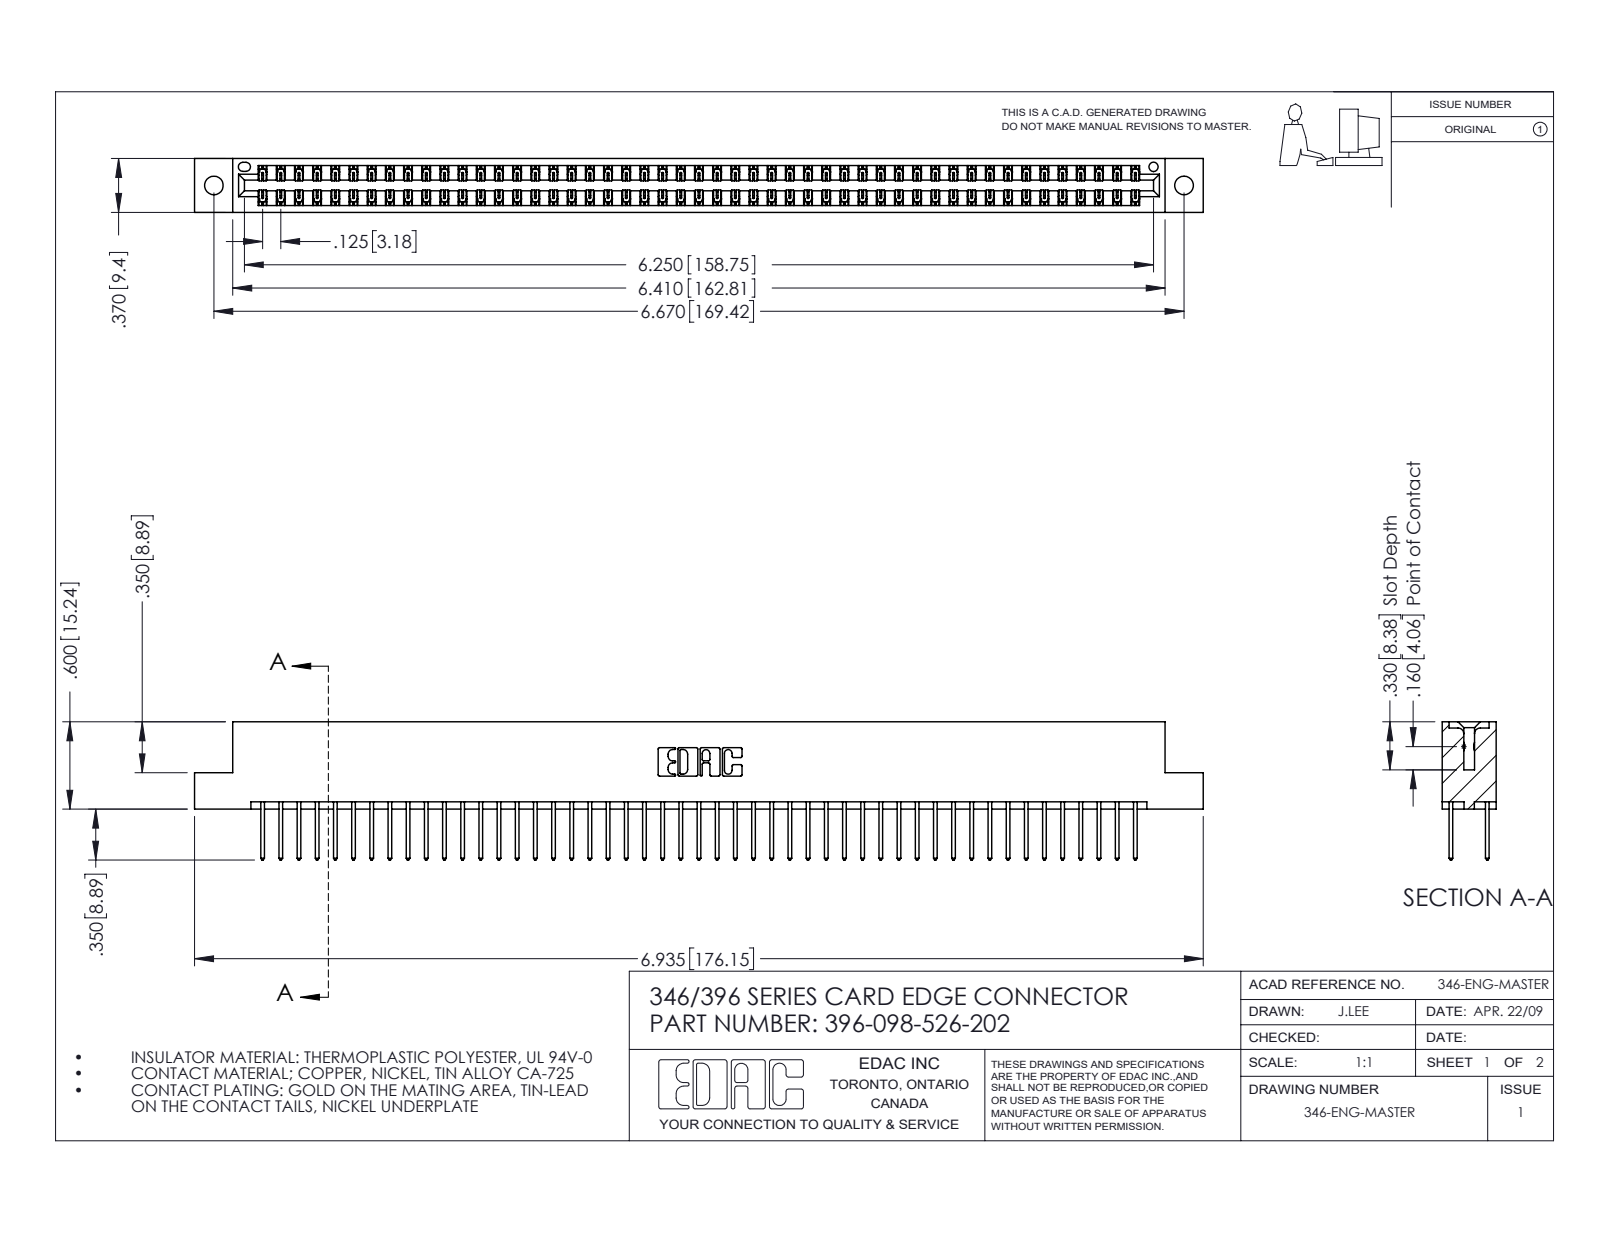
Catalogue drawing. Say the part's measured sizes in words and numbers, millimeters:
The part is named "396-098-526-202; 345-292-001_345-293-126; 346 Part_Flush Mounting Lugs - 0.128 Dia". Its 3-D file was written by "SolidWorks 2016 (CONFIG_CONTROL_DESIGN)". It is 99 solids with 5218 faces: 3506 planar, 1712 cylindrical and 0 other. Overall it measures 176.1 by 24.1 by 9.4 millimeters. Its volume is 17 350 cubic millimeters and its surface area 24 410 square millimeters. Round holes: 2 of diameter 3.3, 1 of diameter 1.6. Partial cylindrical surfaces (rounded edges, fillets, slot ends): 147 of radius 0.2, 98 of radius 0.3, 22 of radius 0.3, 6 of radius 0.2, 6 of radius 0.8, 3 of radius 0.7, 2 of radius 0.4, 2 of radius 0.6. The main face-to-face distances are 1.2, 8.2, 6.4, 9.4, 1.8, 7.6, 0.6, 7, 3.8, 5.6. The hole center spacings are 6.2, 164.1, 169.4.
